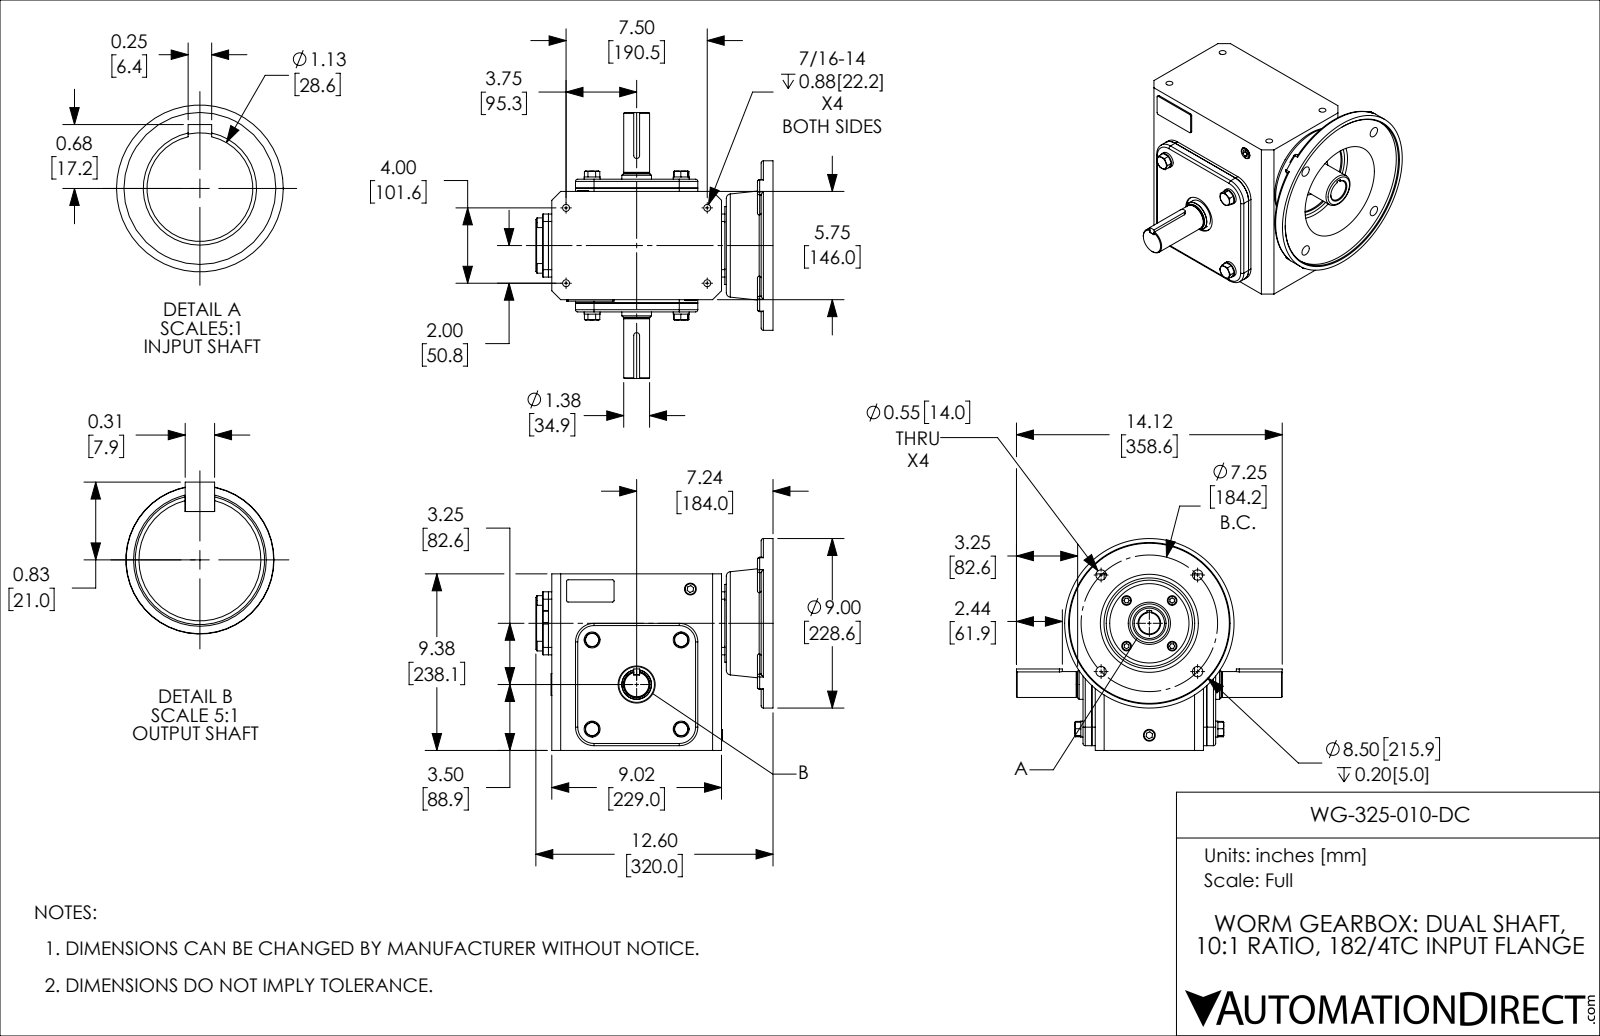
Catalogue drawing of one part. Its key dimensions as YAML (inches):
part_name: "WG-325-010-DC"
step_written_by: "SolidWorks 2017 (AUTOMOTIVE_DESIGN)"
units: inches
bodies: {solids: 43, faces: 690, planar: 349, cylindrical: 206, other: 135}
overall_size: [14.118, 12.598, 11.25]
volume: 542
surface_area: 1065
round_holes:
  - {diameter: 0.354, count: 4}
  - {diameter: 0.368, count: 4}
  - {diameter: 0.551, count: 4}
  - {diameter: 0.628, count: 3}
  - {diameter: 0.591, count: 1}
  - {diameter: 0.978, count: 1}
  - {diameter: 1.125, count: 1}
  - {diameter: 1.181, count: 1}
  - {diameter: 1.969, count: 1}
  - {diameter: 2.244, count: 1}
  - {diameter: 2.441, count: 1}
  - {diameter: 2.756, count: 1}
round_bosses_or_shafts:
  - {diameter: 0.846, count: 4}
  - {diameter: 0.512, count: 4}
  - {diameter: 9, count: 1}
  - {diameter: 4.134, count: 1}
  - {diameter: 2.835, count: 1}
  - {diameter: 1.772, count: 1}
  - {diameter: 1.575, count: 1}
  - {diameter: 1.375, count: 1}
partial_cylinders:
  - {radius: 0.118, count: 18}
  - {radius: 0.079, count: 7}
  - {radius: 0.394, count: 4}
  - {radius: 0.906, count: 4}
  - {radius: 0.984, count: 4}
  - {radius: 0.02, count: 2}
  - {radius: 0.039, count: 2}
  - {radius: 0.156, count: 2}
face_to_face_distances: [0.079, 0.177, 6.496, 0.394, 6.969, 0.472, 6.575, 6.398, 0.571, 0.65]
hole_center_spacings: [4.009, 1.713, 1.913, 2.422, 3.625, 5.127, 5.338, 2.372]
